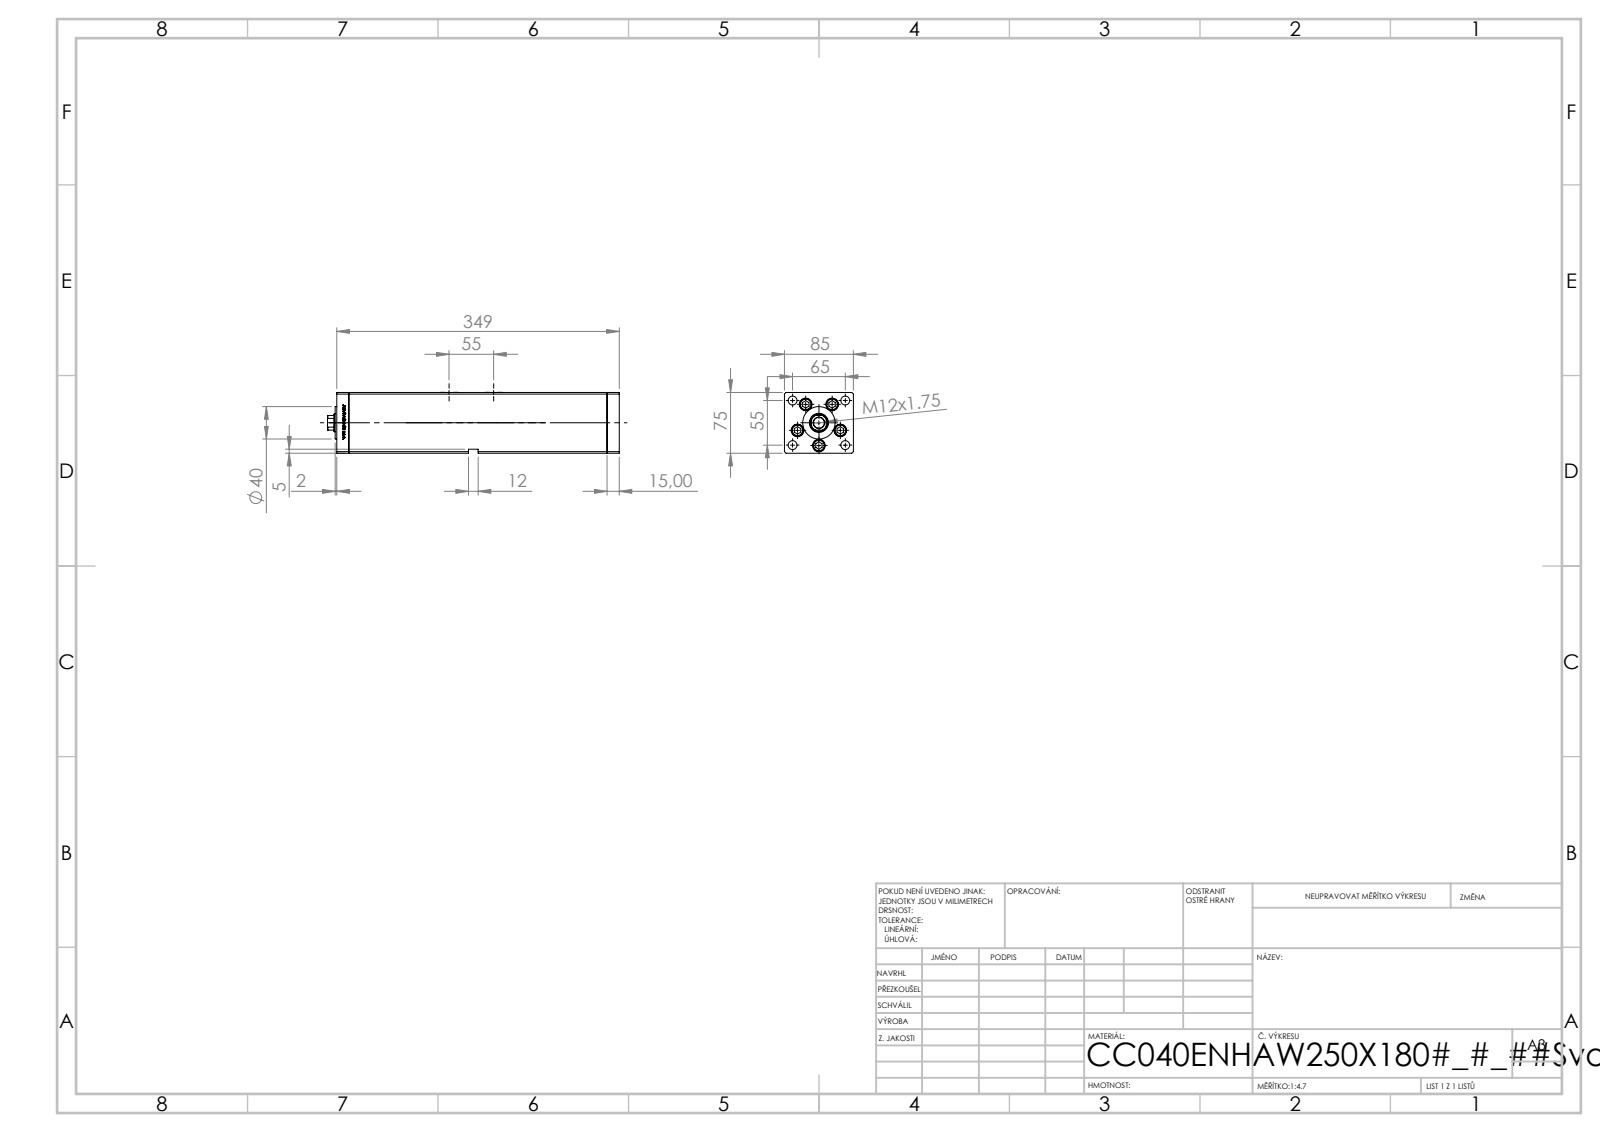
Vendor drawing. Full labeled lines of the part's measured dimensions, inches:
Part name (STEP PRODUCT): V220C_E MIDDLE; V220C BACK_E; V220C_VC_E; ALLEN BOLT (+1 more)
STEP written by: SolidWorks 2019 (CONFIG_CONTROL_DESIGN)
Units: inches
Bodies: 14 solids, 1212 faces (473 planar, 165 cylindrical, 574 other)
Overall size (bounding box): 14.173 × 3.346 × 2.953
Volume: 114.2 in³ · Surface area: 407.6 in²
Round holes (diameter × count): ⌀0.433 ×9, ⌀0.61 ×5, ⌀0.413 ×4, ⌀0.65 ×4, ⌀0.079 ×2, ⌀0.518 ×2, ⌀0.531 ×1, ⌀0.866 ×1, ⌀0.925 ×1
Round bosses / shafts (diameter × count): ⌀0.571 ×5, ⌀0.315 ×5, ⌀1.575 ×1
Partial cylindrical surfaces — rounded edges, fillets, slot ends (radius × count): R0.037 ×2, R0.413 ×1
Main face-to-face distances: 3.346, 2.953, 0.591, 12.539, 13.13, 0.413, 2.539, 1.23, 2.116, 2.697
Hole centre spacings: 1.102, 1.676, 2.165, 2.559, 3.352, 0.664, 0.755, 1.273
